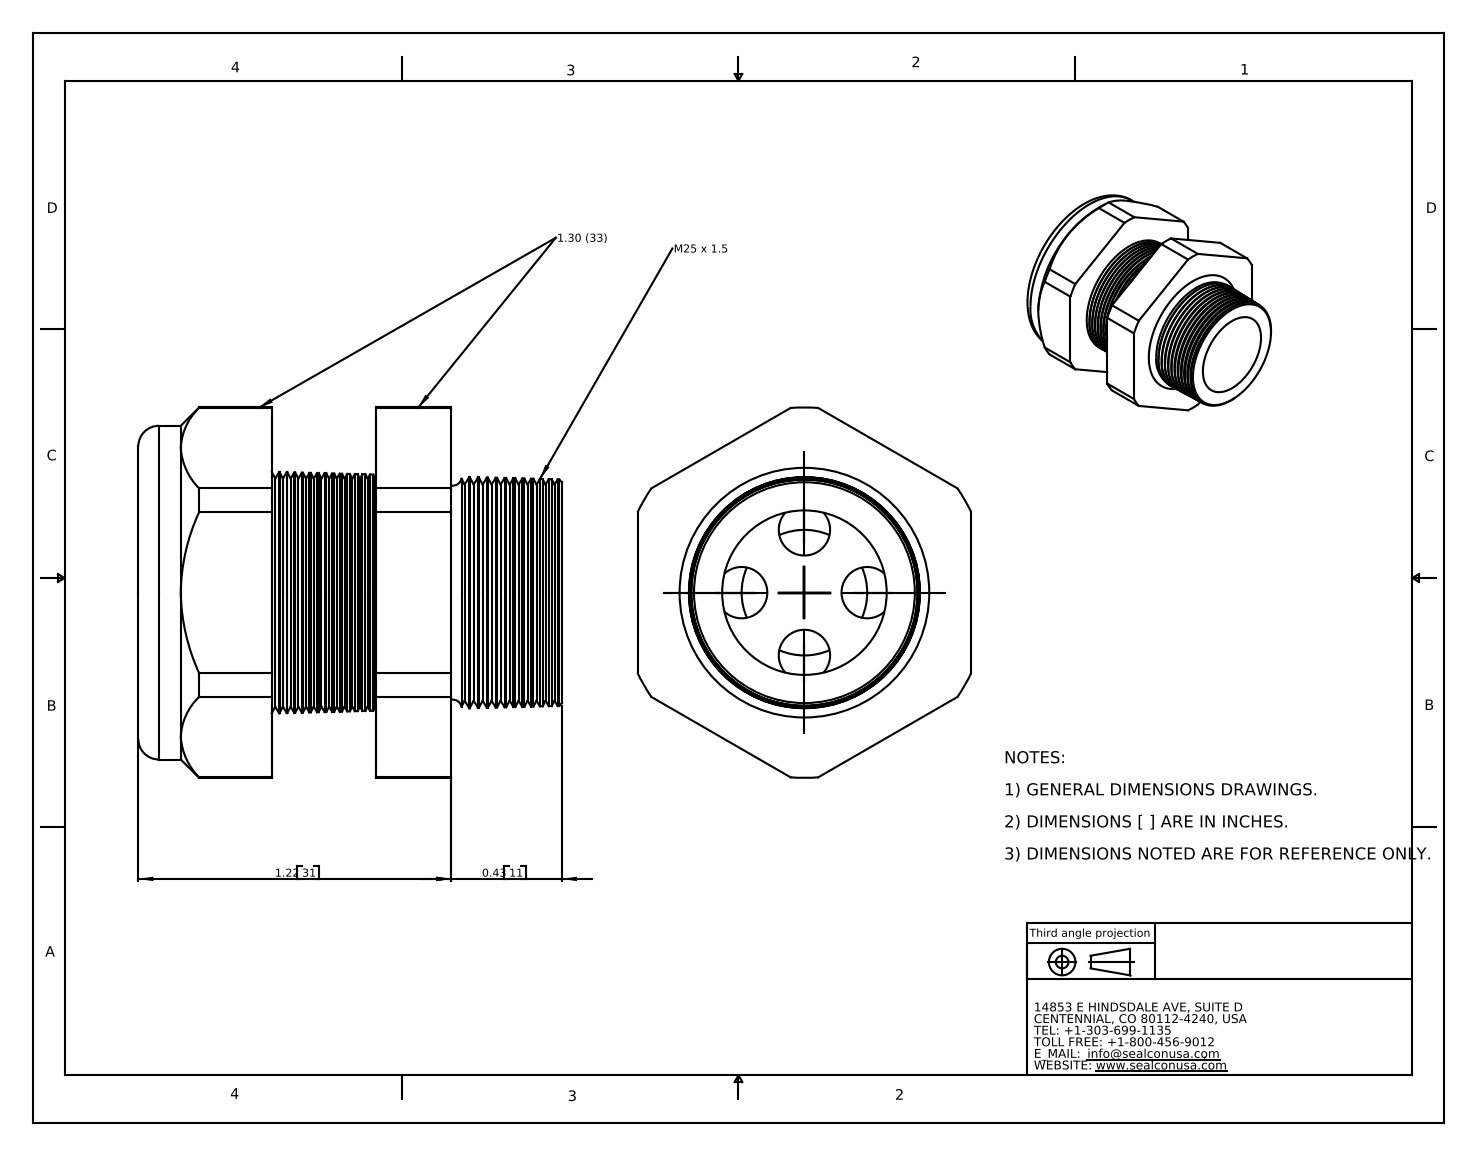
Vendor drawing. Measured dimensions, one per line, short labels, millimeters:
name: CD25M4-BK
written by: SolidWorks 2007 (CONFIG_CONTROL_DESIGN)
unit: mm
bodies: 2 solids, 214 faces (20 planar, 28 cylindrical, 166 other)
size: 41.9 × 36.7 × 33
volume: 18 850 mm³; area: 11 050 mm²
holes: 4× ⌀5.1, 1× ⌀17.5, 1× ⌀18
bosses: 1× ⌀33
rounds: 1× R18.3
face distances: 33, 10.3, 17.8, 7.5, 13.2, 23.5, 31, 8.9, 4.3, 14.6
hole spacings: 6.2, 8.8, 12.4
